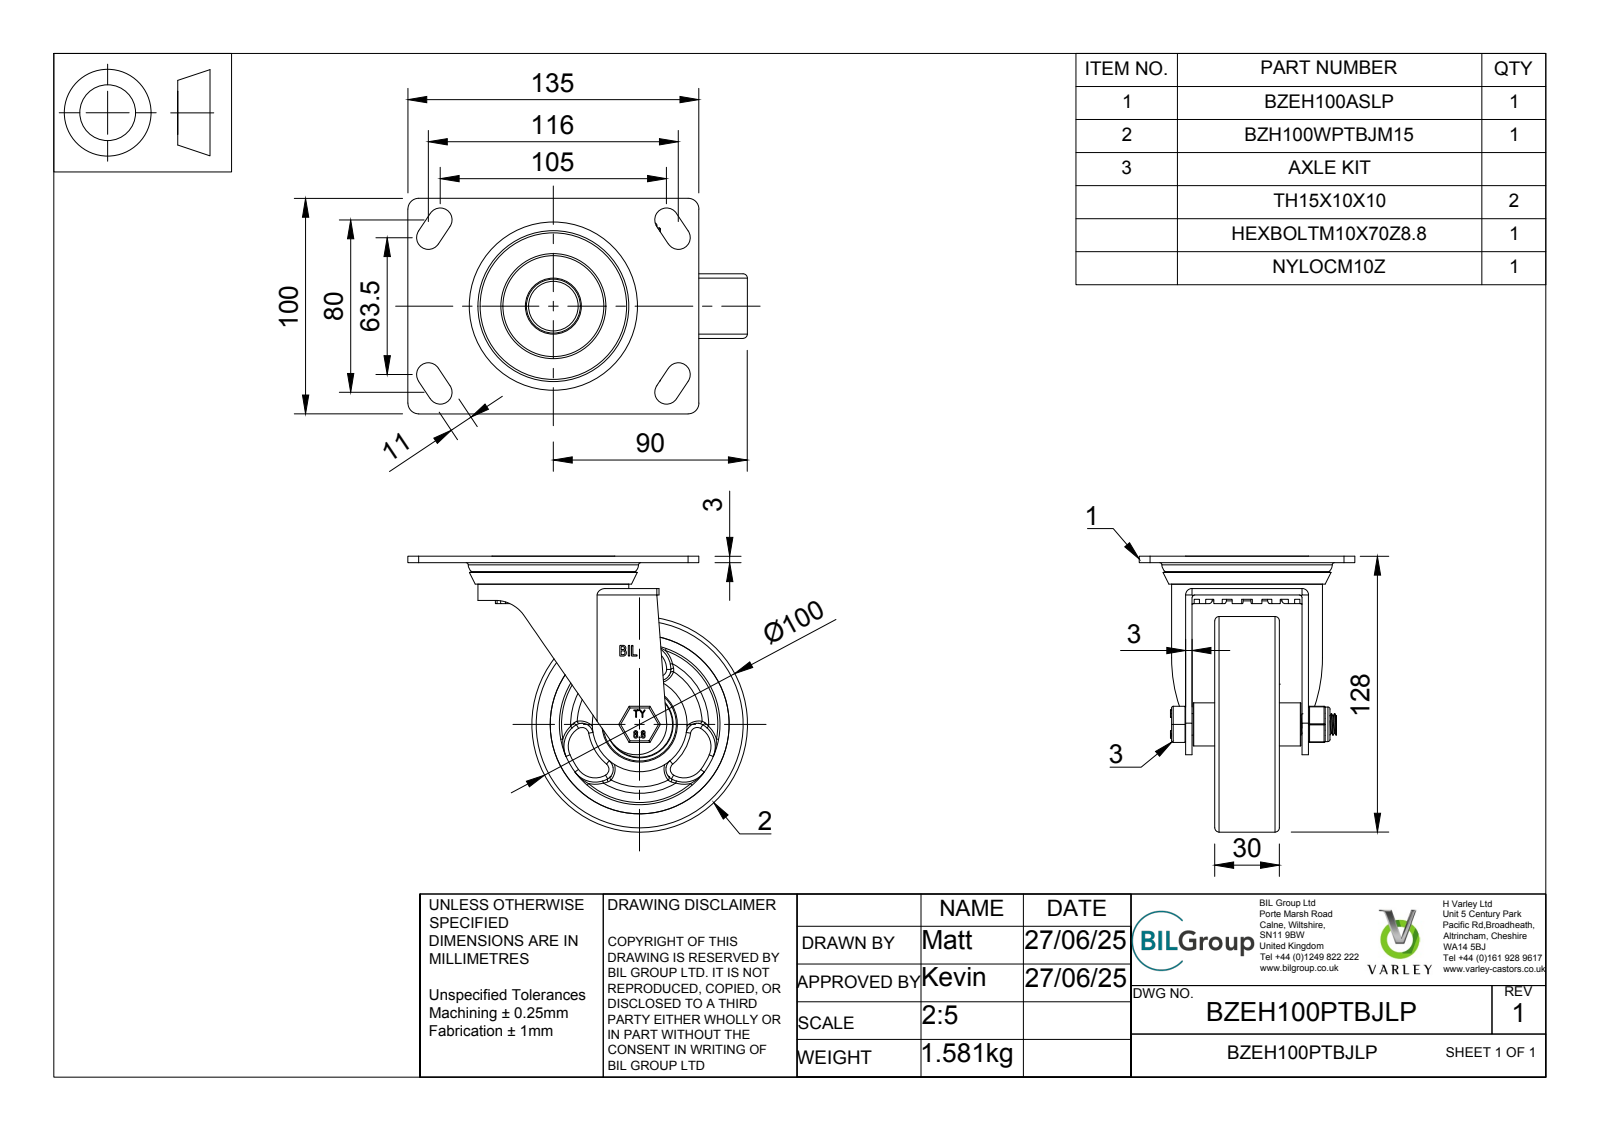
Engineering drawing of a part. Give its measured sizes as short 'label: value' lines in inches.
name: BZEH100PTBJLP v3; BZEH100ASLP v1; ZINC PLATED, PRESSED STEEL TOP PLATE; ZINC PLATED, PRESSED STEEL TOP PLATE Geometry (+7 more)
written by: Autodesk Translation Framework v14.10.0.0 (AUTOMOTIVE_DESIGN)
unit: in
bodies: 57 solids, 1329 faces (519 planar, 225 cylindrical, 585 other)
size: 6.201 × 5.039 × 3.937
volume: 16.8 in³; area: 226.8 in²
holes: 2× ⌀1.181, 1× ⌀0.394, 1× ⌀0.402, 1× ⌀0.413, 1× ⌀0.472, 1× ⌀0.591, 1× ⌀0.886, 1× ⌀1.22, 1× ⌀1.26, 1× ⌀1.378, 1× ⌀2.52, 1× ⌀2.933
bosses: 1× ⌀3.937, 1× ⌀2.756, 1× ⌀2.126, 1× ⌀1.732, 1× ⌀1.201, 1× ⌀0.984, 1× ⌀0.906, 1× ⌀0.827
rounds: 18× R0.02, 12× R0.202, 12× R0.458, 8× R0.217, 6× R0.03, 4× R0.197, 3× R0.049, 2× R0.118
face distances: 0.118, 0.394, 0.197, 0.413, 2.126, 0.079, 0.531, 1.713, 0.315, 1.181
